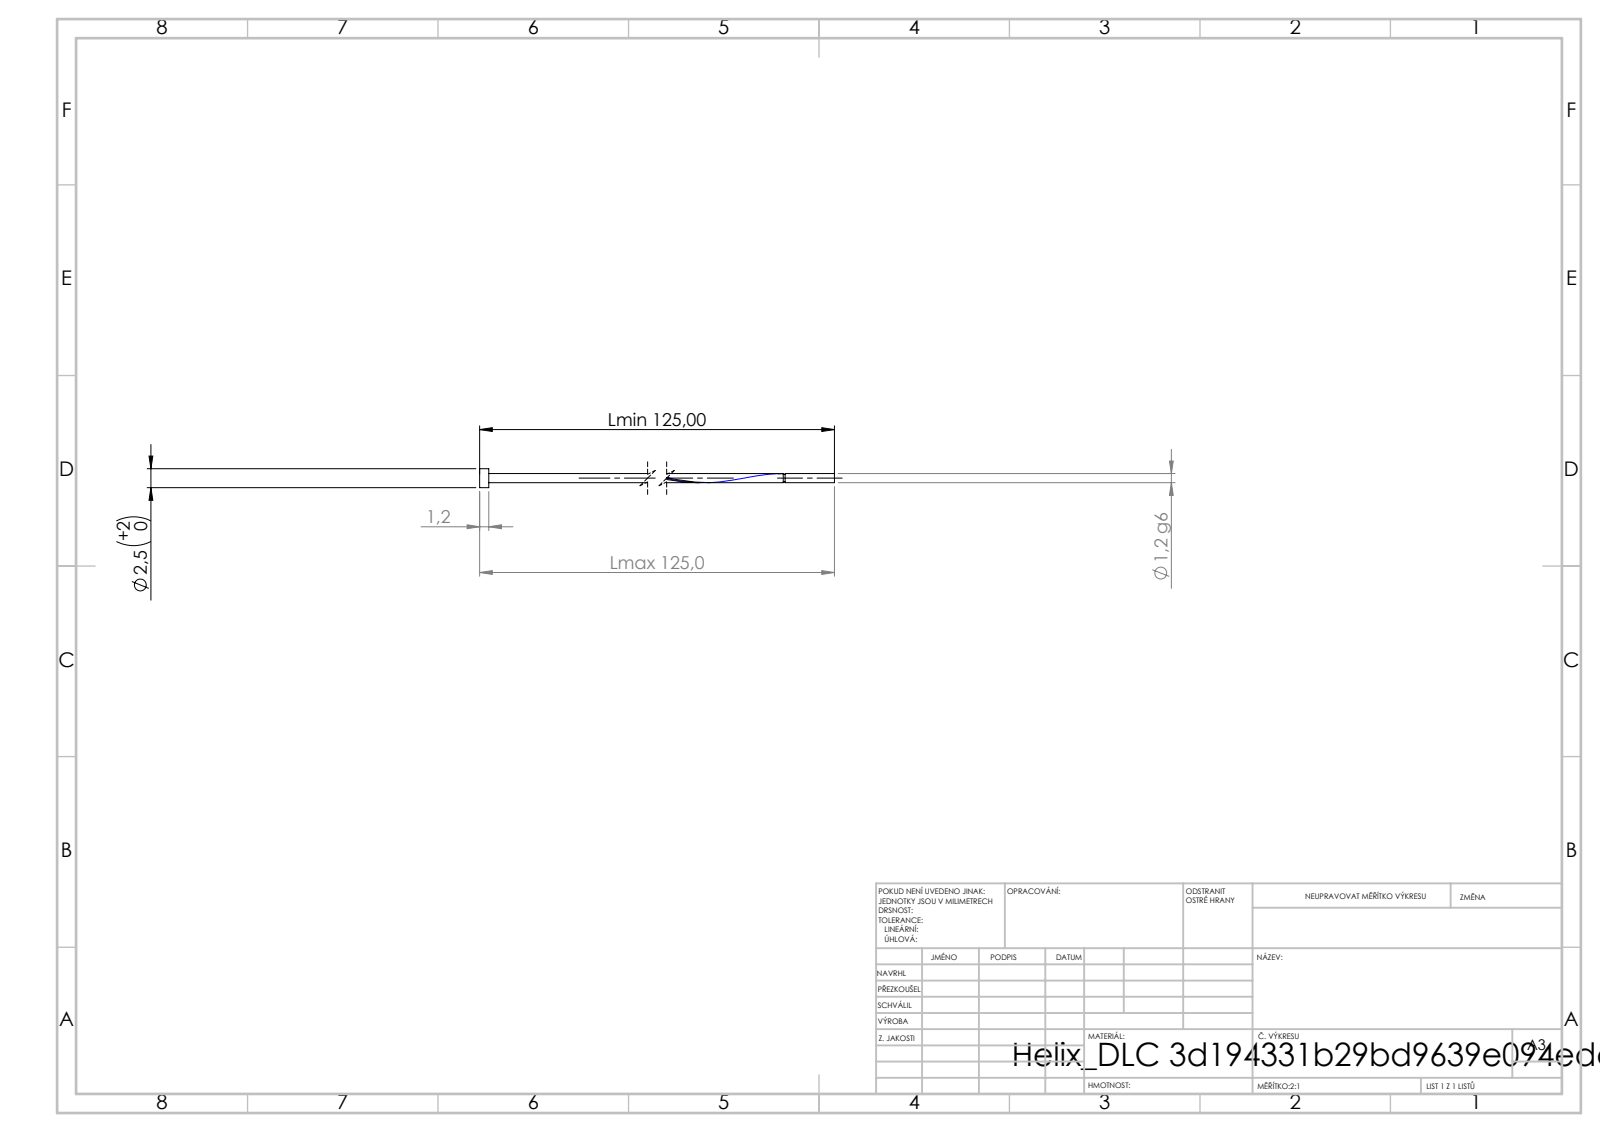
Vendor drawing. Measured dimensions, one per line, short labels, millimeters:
written by: SolidWorks 2019 (CONFIG_CONTROL_DESIGN)
unit: mm
bodies: 1 solid, 16 faces (6 planar, 9 cylindrical, 1 other)
size: 125 × 2.5 × 2.5
volume: 176 mm³; area: 651 mm²
bosses: 1× ⌀2.5, 1× ⌀1.2, 1× ⌀0.96
face distances: 1.2, 125, 123.8, 118.52, 117.32, 6.48, 118.28, 117.08, 6.72, 55.78
